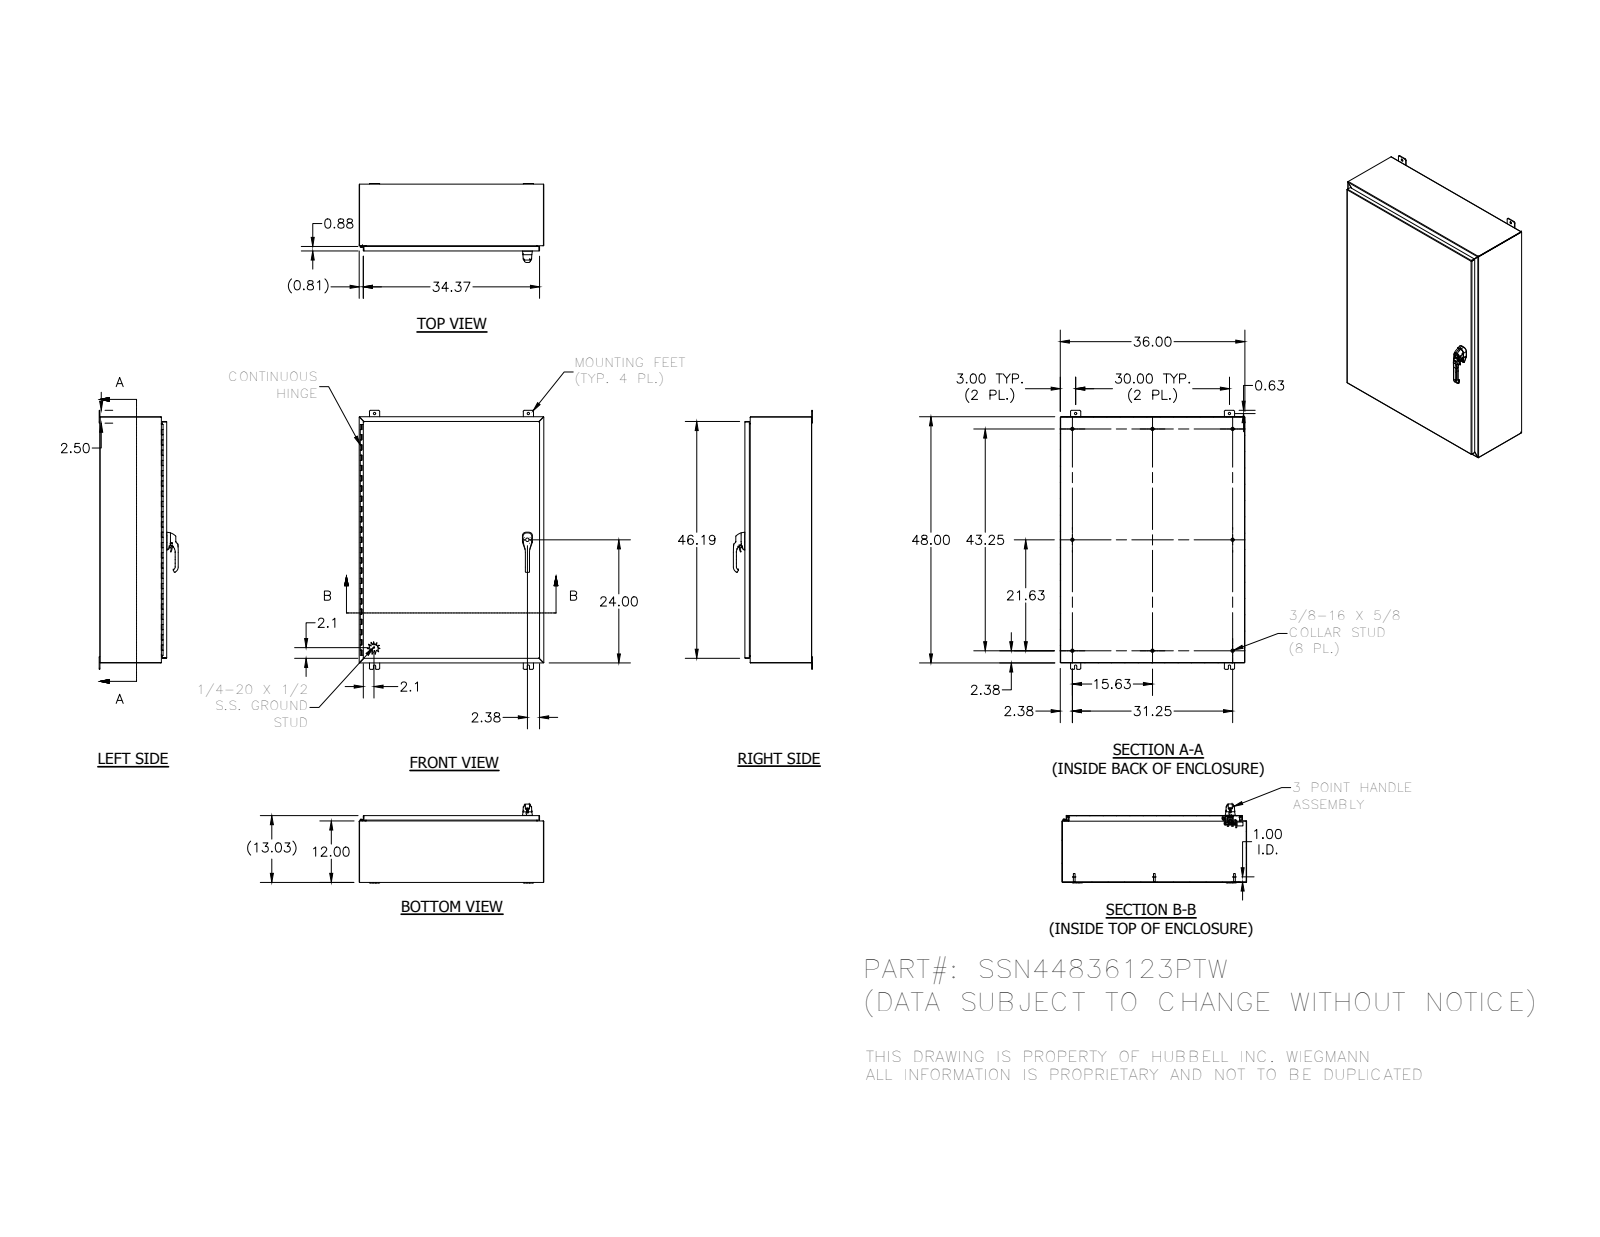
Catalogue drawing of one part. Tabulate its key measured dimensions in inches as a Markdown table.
| quantity | value |
| --- | --- |
| part name | 46x34; PLASTIC-ROLLER-CAM_AF1; DIN985_M10; 32874-48L (+8 more) |
| STEP written by | SolidWorks 2014 (AUTOMOTIVE_DESIGN) |
| units | inches |
| bodies | 62 solids, 3345 faces (1192 planar, 1368 cylindrical, 785 other) |
| overall size | 50.5 × 36 × 15.408 |
| volume | 471.4 in³ |
| surface area | 12 441 in² |
| round holes (diameter × count) | 0.262 × 8, 0.187 × 4, 0.438 × 4, 0.213 × 3, 0.281 × 3, 0.241 × 2, 0.25 × 2, 0.252 × 2, 0.315 × 2, 0.4 × 2, 0.402 × 2, 0.413 × 2 |
| round bosses / shafts (diameter × count) | 0.625 × 8, 0.33 × 8, 0.236 × 3, 1 × 2, 0.563 × 2, 0.533 × 2, 0.531 × 2, 0.5 × 2 |
| partial cylindrical surfaces (radius × count) | 0.02 × 172, 0.012 × 113, 0.125 × 26, 0.031 × 22, 0.019 × 21, 0.25 × 20, 0.105 × 18, 0.05 × 15 |
| main face-to-face distances | 0.074, 12.959, 12.885, 13.033, 35.926, 47.926, 35.852, 36, 47.852, 48 |
| hole center spacings | 0.38, 0.492, 0.76, 0.886, 38.428, 0.234, 0.258, 0.38 |
